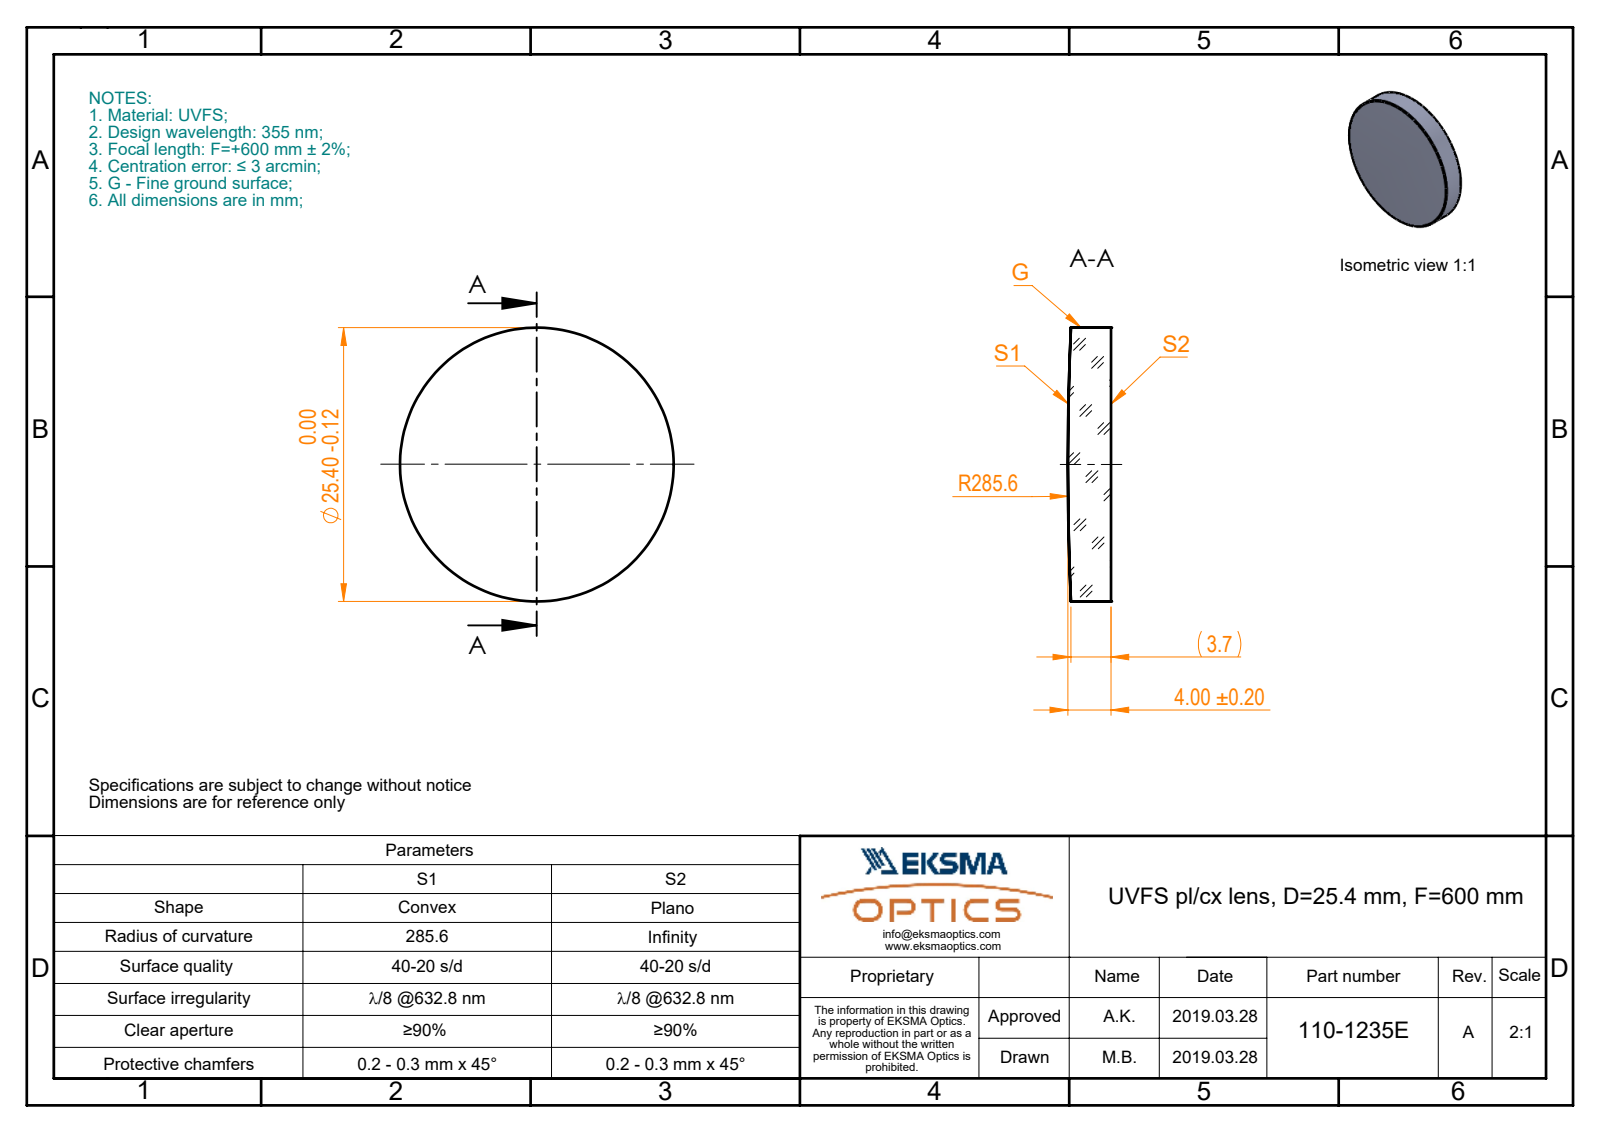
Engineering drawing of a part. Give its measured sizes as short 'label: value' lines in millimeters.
name: 110-1235E UVFS pl-cx 25.4 F600
written by: SolidWorks 2017 (CONFIG_CONTROL_DESIGN)
unit: mm
bodies: 1 solid, 5 faces (1 planar, 2 cylindrical, 2 other)
size: 25.4 × 25.4 × 4
volume: 1 955 mm³; area: 1 310 mm²
bosses: 1× ⌀25.4
